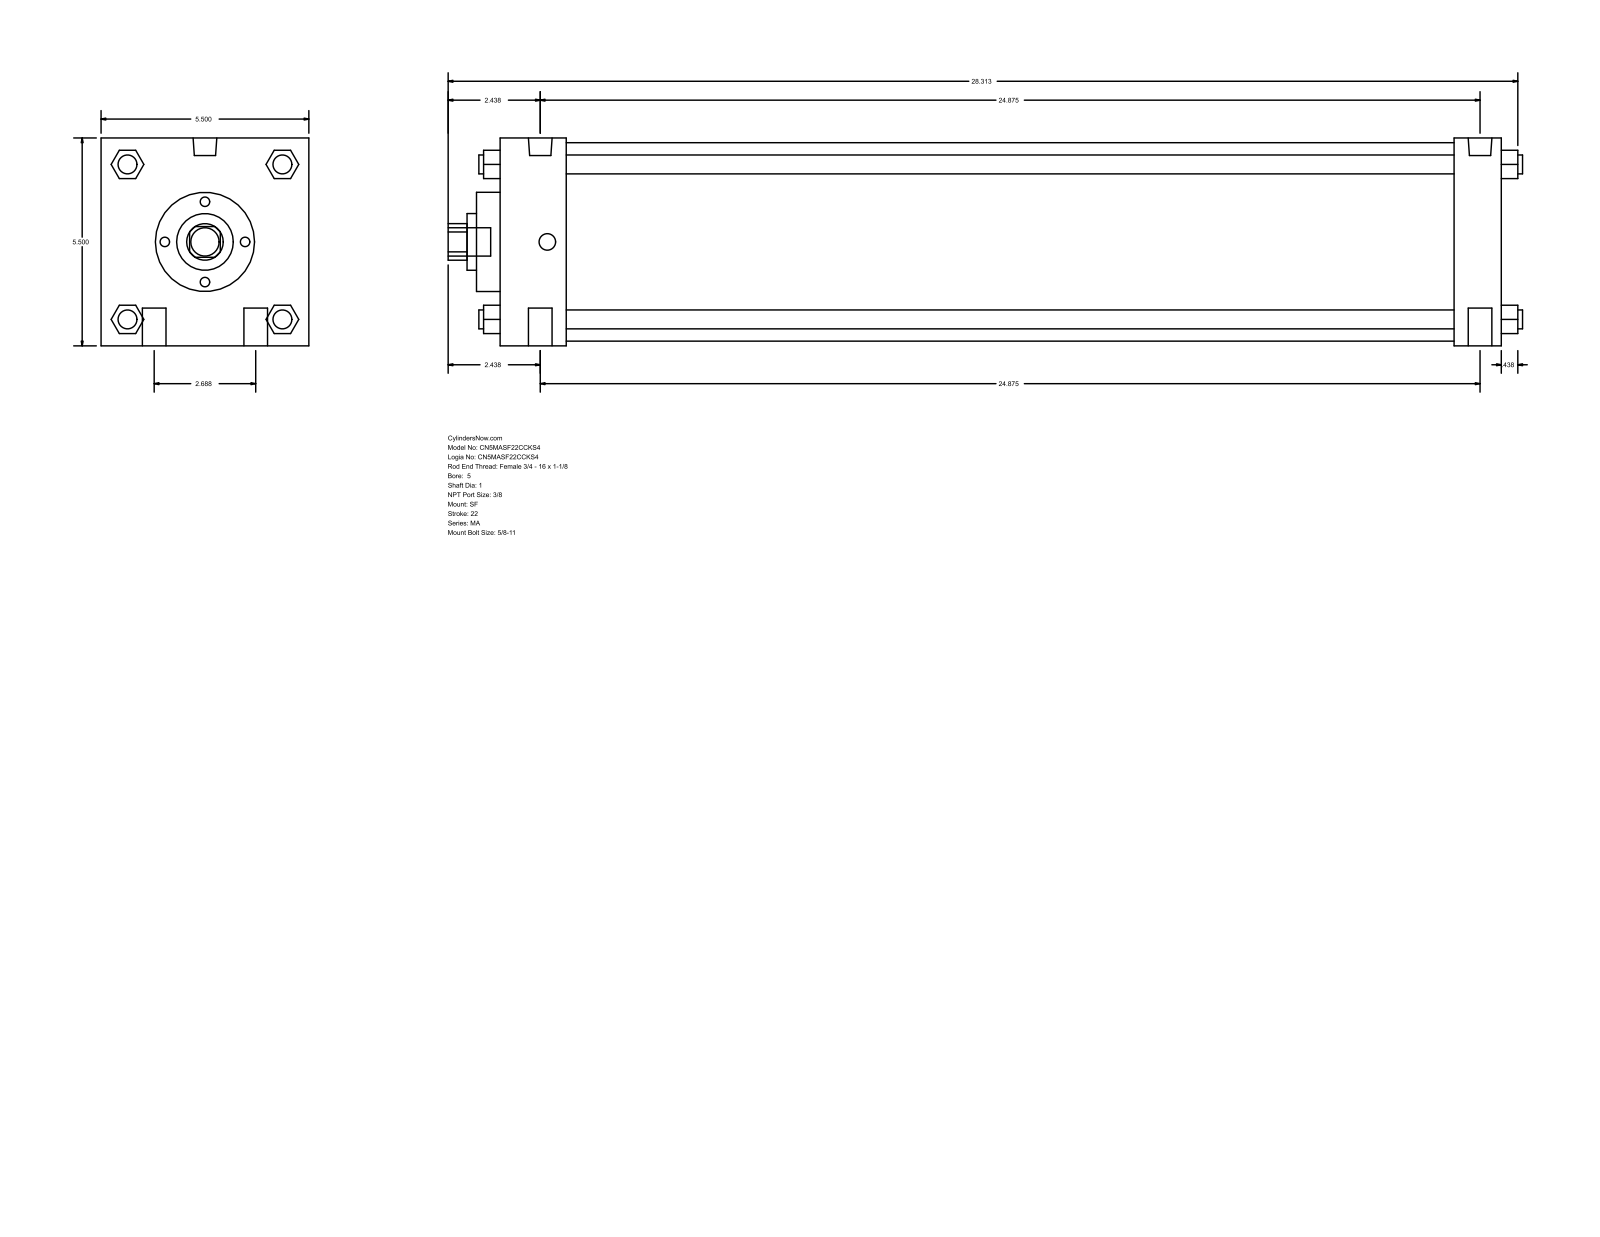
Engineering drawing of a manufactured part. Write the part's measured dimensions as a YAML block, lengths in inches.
part_name: "MA_SF__0500_1"
step_written_by: "GSSL Pune (CONFIG_CONTROL_DESIGN)"
units: inches
bodies: {solids: 0, faces: 126, planar: 95, cylindrical: 31, other: 0}
overall_size: [28.437, 5.5, 5.5]
round_holes:
  - {diameter: 1, count: 1}
  - {diameter: 1.5, count: 1}
  - {diameter: 2.625, count: 1}
  - {diameter: 5.25, count: 1}
round_bosses_or_shafts:
  - {diameter: 0.625, count: 4}
  - {diameter: 0.5, count: 4}
  - {diameter: 0.627, count: 2}
  - {diameter: 0.437, count: 2}
  - {diameter: 0.75, count: 1}
partial_cylinders:
  - {radius: 0.484, count: 1}
face_to_face_distances: [5.5, 26.5, 1.75, 25.25, 23.5, 24.75, 1.25, 0.625, 2.375, 25.875]
